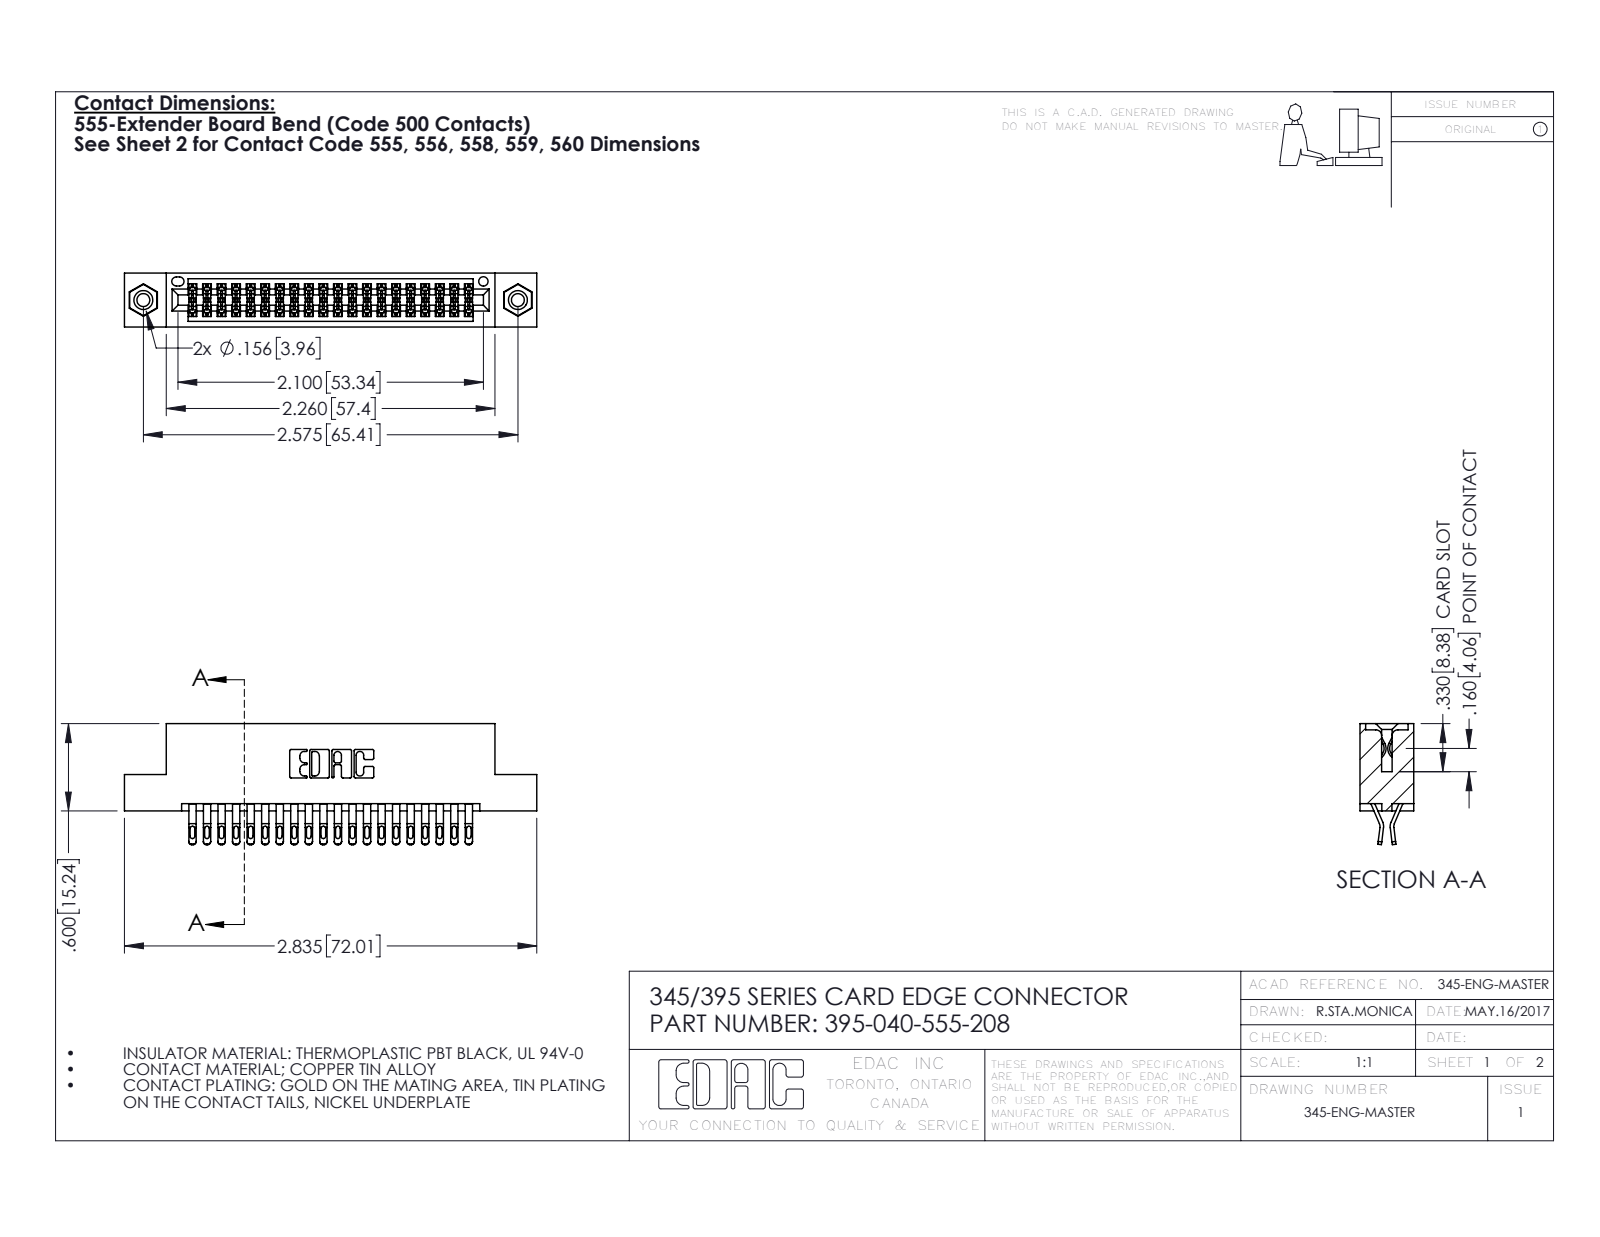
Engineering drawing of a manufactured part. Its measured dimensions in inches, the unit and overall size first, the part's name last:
Units: inches
Overall size (bounding box): 2.835 × 0.832 × 0.37
Round holes (diameter × count): ⌀0.089 ×2, ⌀0.125 ×2, ⌀0.156 ×2, ⌀0.064 ×1
Round bosses / shafts (diameter × count): ⌀0.155 ×2
Partial cylindrical surfaces — rounded edges, fillets, slot ends (radius × count): R0.016 ×100, R0.02 ×80, R0.006 ×60, R0.01 ×22, R0.007 ×6, R0.031 ×6, R0.026 ×3, R0.01 ×2
Main face-to-face distances: 0.072, 0.298, 0.2, 0.37, 0.025, 0.098, 0.272, 0.225, 0.175, 0.149
Hole centre spacings: 0.27, 2.341, 2.575
Volume: 0.421 in³ · Surface area: 15.8 in²
Bodies: 43 solids, 2426 faces (1352 planar, 1058 cylindrical, 16 other)
Part name (STEP PRODUCT): 345-292-001_555 Tail; 345-250-001_345-250-003-102; 345 Part_Flush Mounting Lugs - 0.156 Dia-TI; 395-040-555-208
STEP written by: SolidWorks 2016 (CONFIG_CONTROL_DESIGN)
